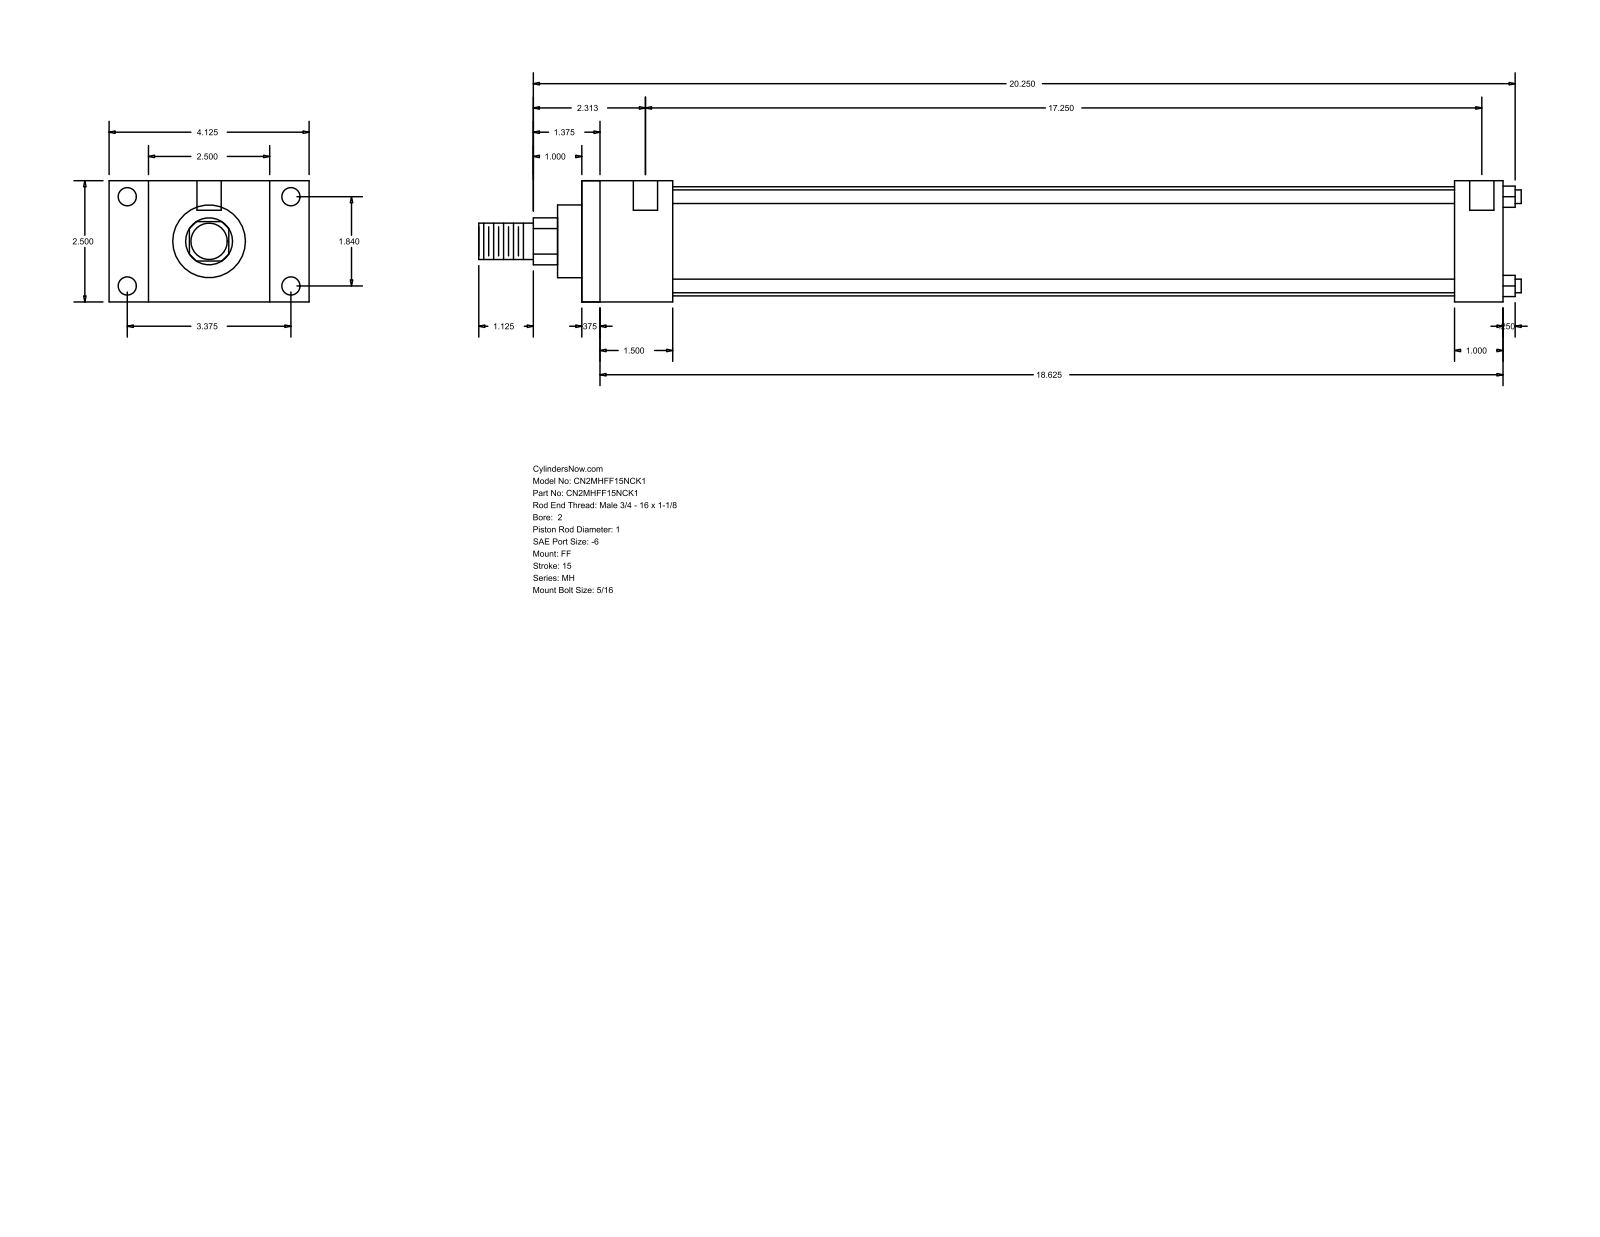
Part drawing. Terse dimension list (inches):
name: MH_FF__0200_1
written by: GSSL Pune (CONFIG_CONTROL_DESIGN)
unit: in
bodies: 0 solids, 92 faces (64 planar, 28 cylindrical, 0 other)
size: 21.5 × 4.125 × 2.5
holes: 4× ⌀0.219, 4× ⌀0.375, 2× ⌀0.5
bosses: 4× ⌀0.281, 1× ⌀2.25, 1× ⌀1.5, 1× ⌀1, 1× ⌀0.75
rounds: 1× R0.484
face distances: 2.5, 19, 0.375, 18.625, 0.813, 1, 1.875, 18, 1.5, 17.625
hole spacings: 1.84, 3.375, 3.844, 17.562, 0.125, 0.187, 17.25, 17.375
